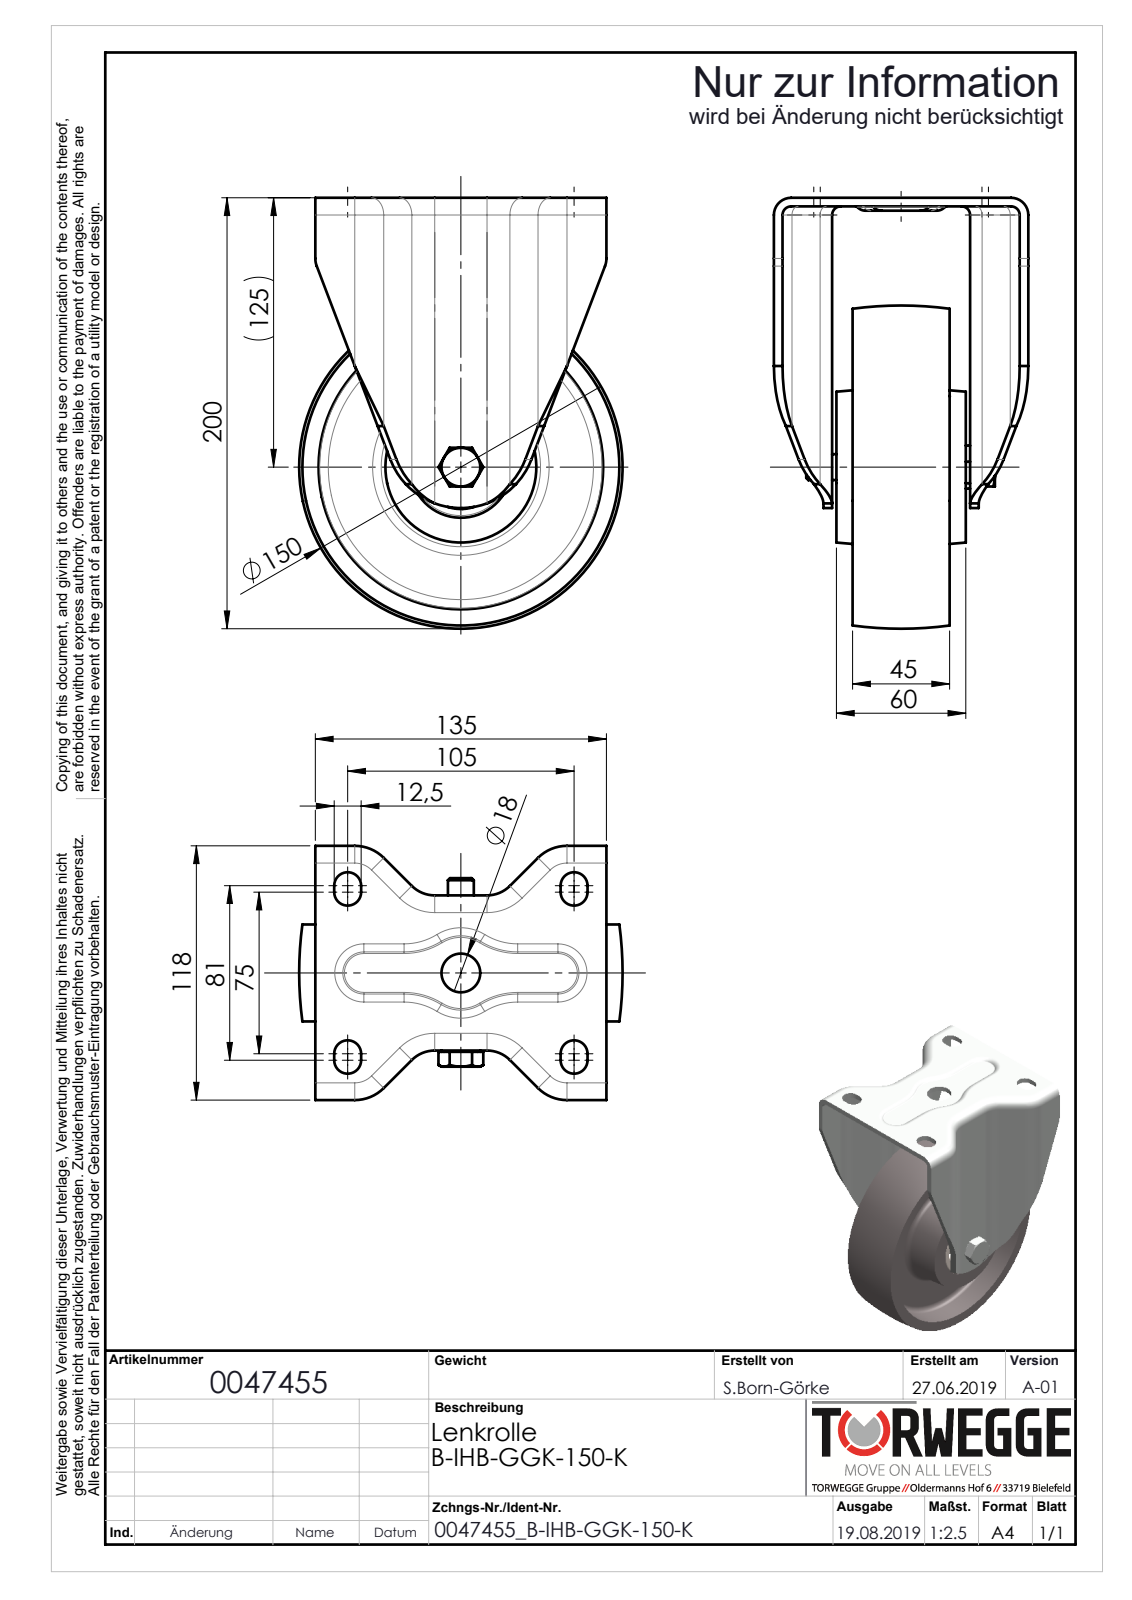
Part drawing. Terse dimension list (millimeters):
name: 0047455_B-IHB-GGK-150-K_(A-01)
written by: SolidWorks 2018 (AUTOMOTIVE_DESIGN)
unit: mm
bodies: 18 solids, 414 faces (119 planar, 138 cylindrical, 157 other)
size: 200 × 150 × 118
volume: 641 399 mm³; area: 216 870 mm²
holes: 1× ⌀10.2, 1× ⌀12, 1× ⌀12.5, 1× ⌀18, 1× ⌀20, 1× ⌀21, 1× ⌀28.1, 1× ⌀38.9, 1× ⌀43, 1× ⌀47
bosses: 1× ⌀25, 1× ⌀18
rounds: 8× R4, 8× R6.25, 8× R8, 8× R15, 8× R19, 4× R1, 4× R5, 2× R10
face distances: 4, 2, 13.5, 20.96, 6, 32, 40, 18.5, 23, 91
